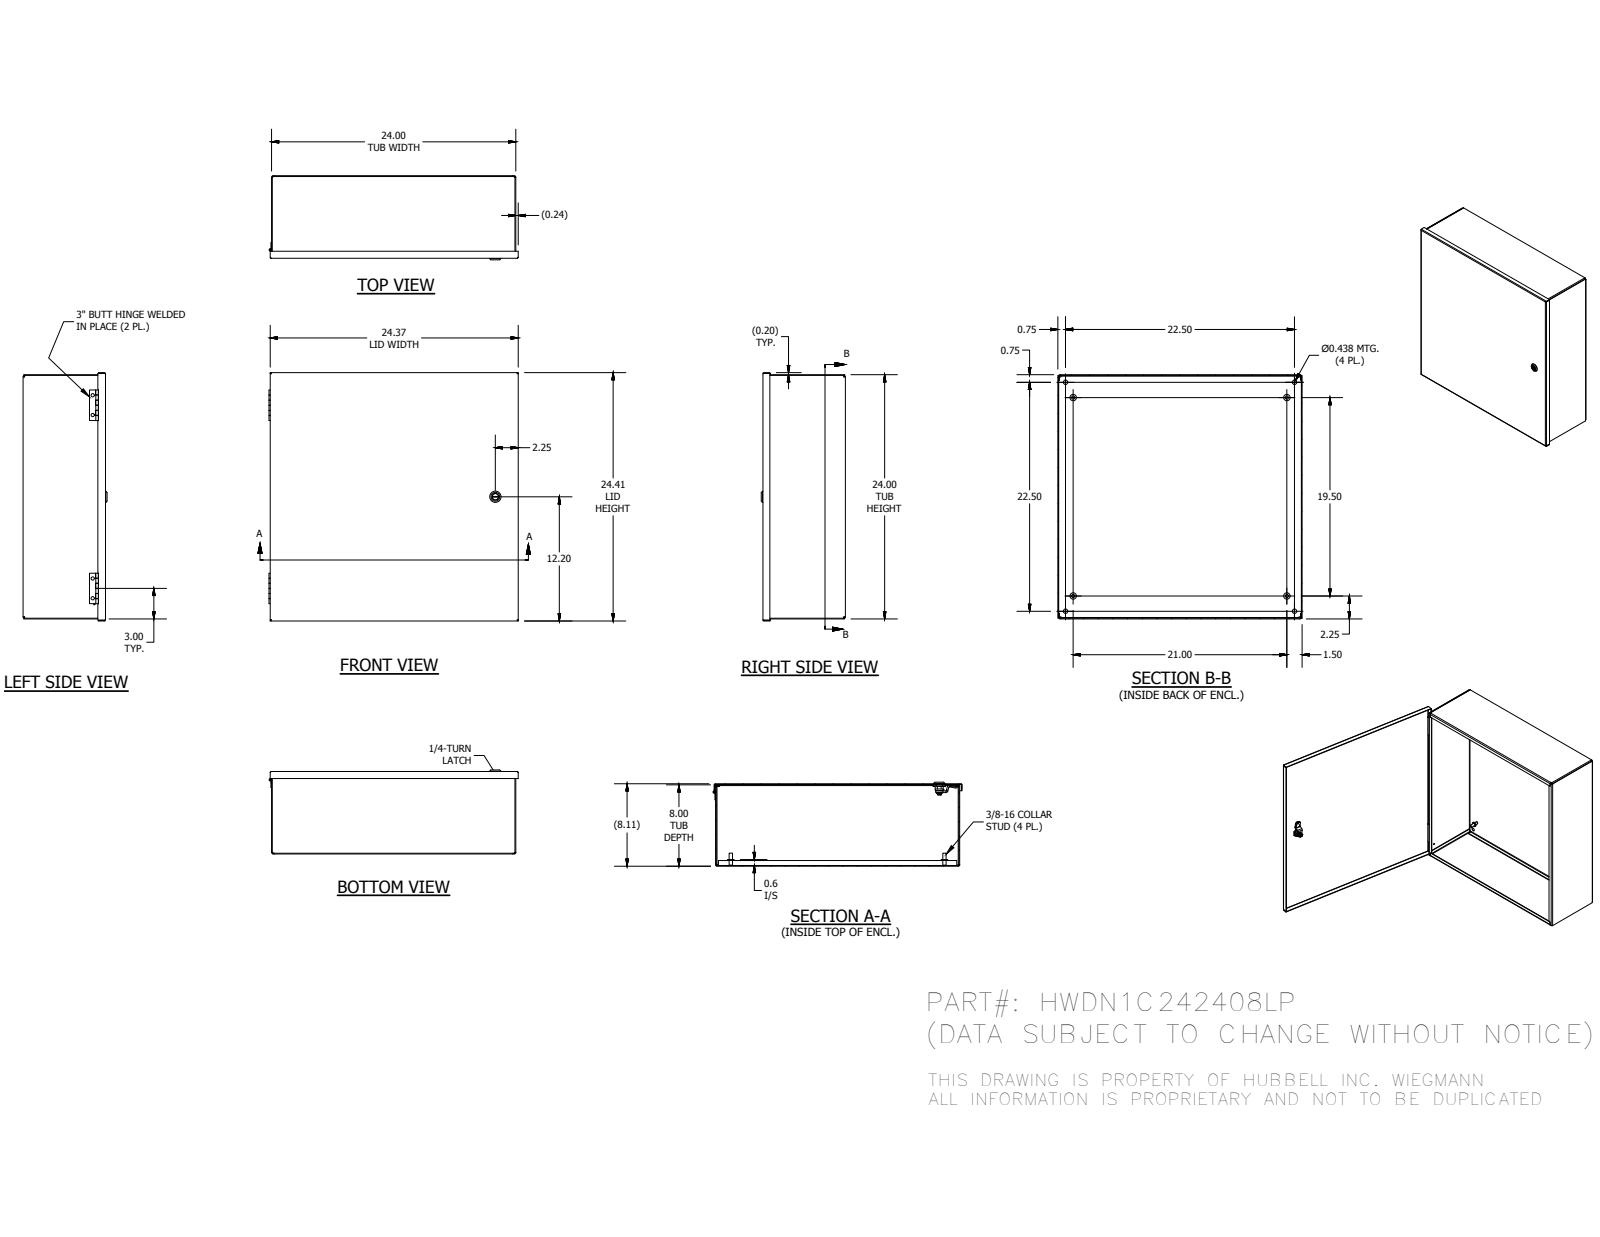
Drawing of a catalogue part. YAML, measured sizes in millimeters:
part_name: "N1C242408LPBLR; N1C2408LPTB; N1C2424LPLID; 1000-101-GPF_GPD (+8 more)"
step_written_by: "Autodesk Inventor 2016 (AUTOMOTIVE_DESIGN)"
units: millimeters
bodies: {solids: 21, faces: 717, planar: 437, cylindrical: 212, other: 68}
overall_size: [622.01, 619.92, 228.92]
volume: 2612000
surface_area: 2795000
round_holes:
  - {diameter: 7.95, count: 4}
  - {diameter: 11.11, count: 4}
  - {diameter: 3.05, count: 1}
  - {diameter: 3.3, count: 1}
  - {diameter: 5, count: 1}
  - {diameter: 8, count: 1}
  - {diameter: 10, count: 1}
  - {diameter: 10.2, count: 1}
  - {diameter: 16.1, count: 1}
  - {diameter: 20.38, count: 1}
round_bosses_or_shafts:
  - {diameter: 15.88, count: 4}
  - {diameter: 8.38, count: 4}
  - {diameter: 28, count: 1}
  - {diameter: 27, count: 1}
  - {diameter: 23, count: 1}
  - {diameter: 19.8, count: 1}
  - {diameter: 15.8, count: 1}
  - {diameter: 15.2, count: 1}
partial_cylinders:
  - {radius: 0.3, count: 30}
  - {radius: 1.59, count: 12}
  - {radius: 3.47, count: 12}
  - {radius: 0.5, count: 10}
  - {radius: 0.79, count: 4}
  - {radius: 2.67, count: 4}
  - {radius: 4, count: 4}
  - {radius: 0.4, count: 3}
face_to_face_distances: [1.88, 223.04, 607.72, 221.16, 224.92, 605.84, 609.6, 220.37, 2.67, 5.16]
hole_center_spacings: [571.5, 49.28, 287.54, 457.2, 610.47, 808.22, 15.51, 64.39]
